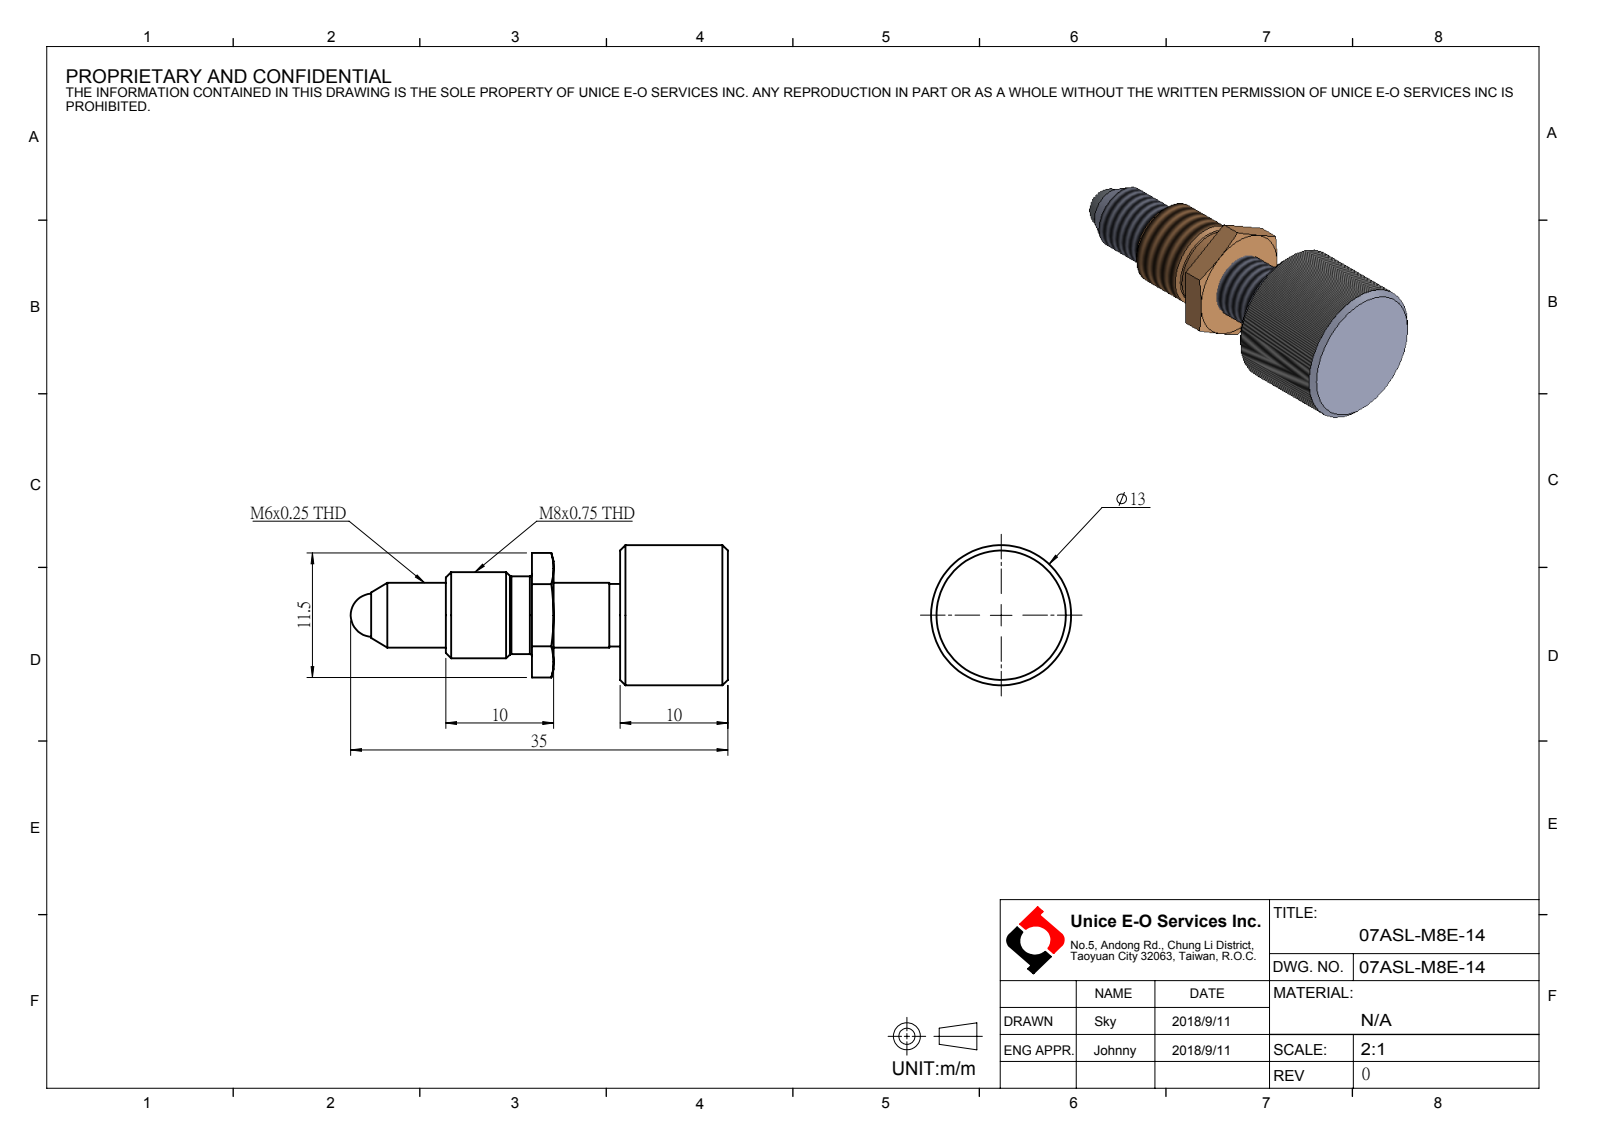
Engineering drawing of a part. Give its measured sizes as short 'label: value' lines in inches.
name: 07ASL-M8E-14
written by: SolidWorks 2016 (AUTOMOTIVE_DESIGN)
unit: in
bodies: 0 solids, 44 faces (12 planar, 10 cylindrical, 22 other)
size: 1.378 × 0.512 × 0.512
bosses: 1× ⌀0.512, 1× ⌀0.315, 1× ⌀0.283, 1× ⌀0.236, 1× ⌀0.228
face distances: 0.394, 0.637, 0.243, 0.079, 0.322, 0.716, 0.315, 1.031, 0.272, 0.587
